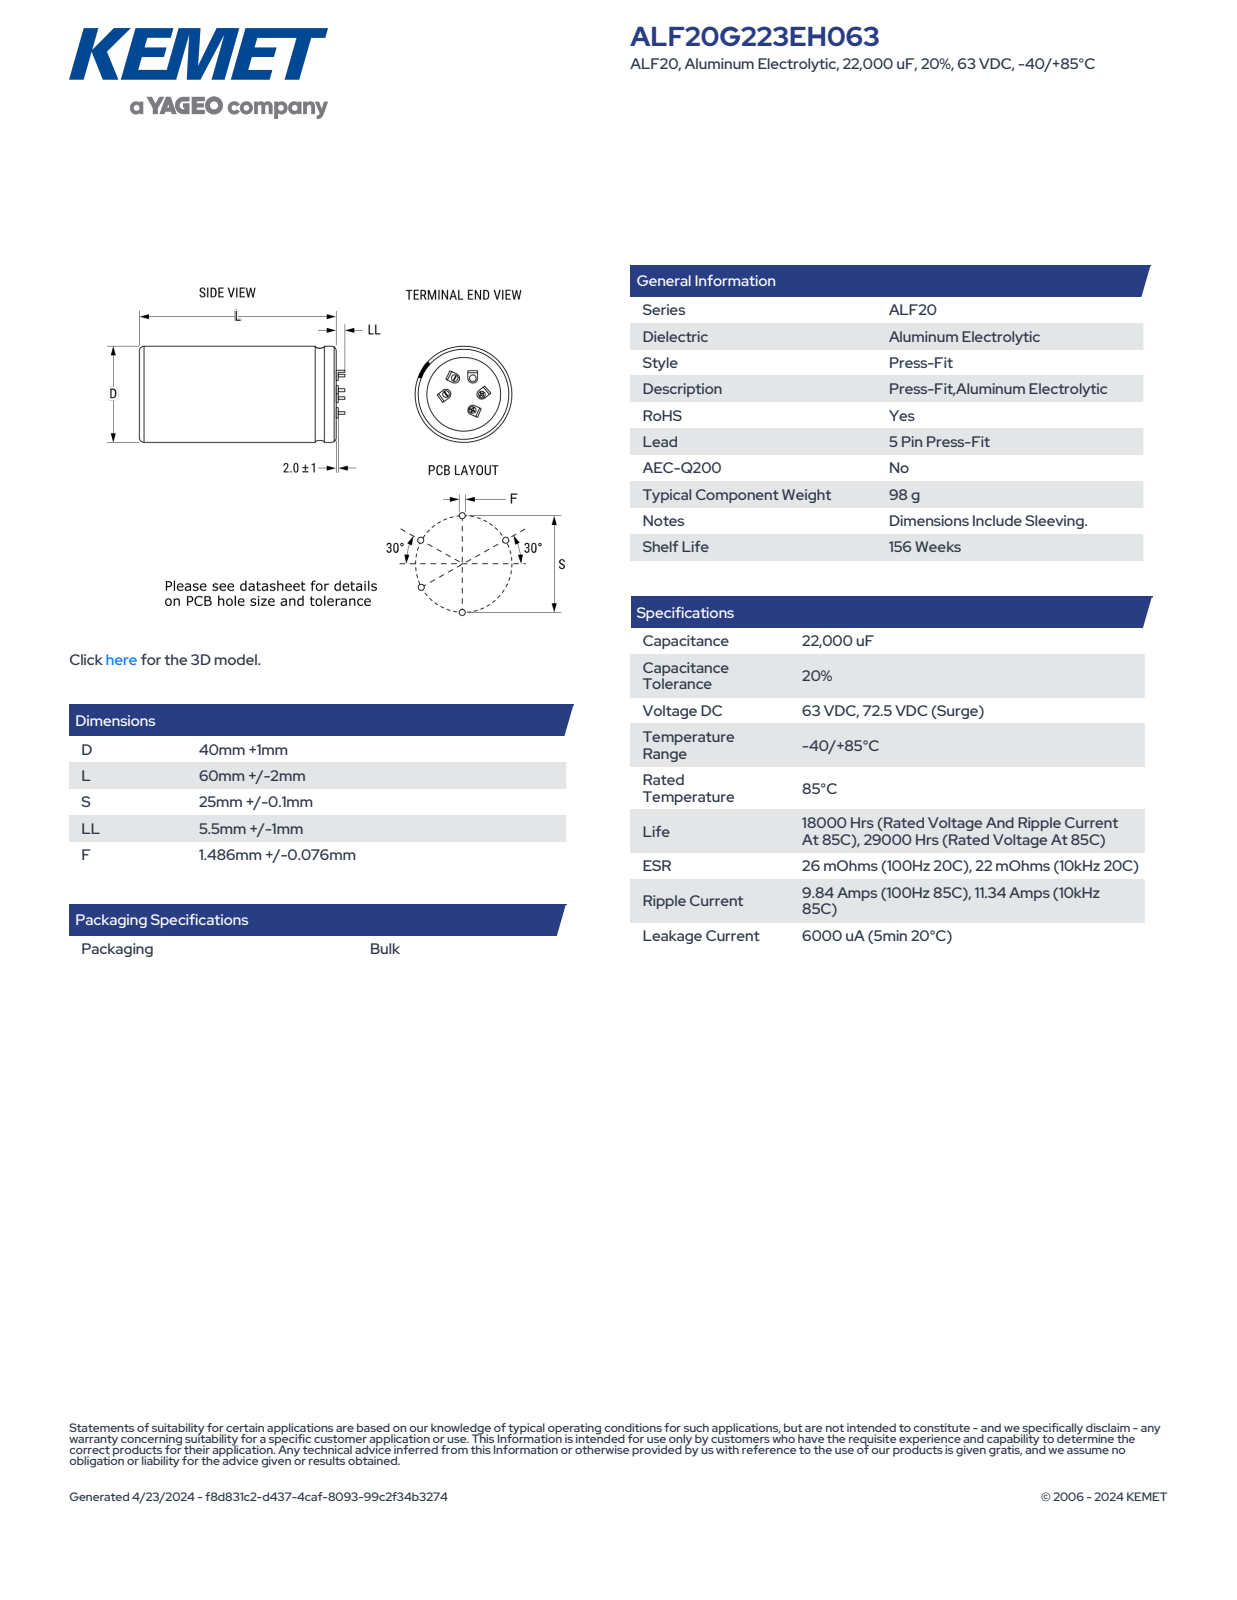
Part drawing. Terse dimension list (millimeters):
name: CARS_ALF2040G_40X60_D41L62S25LL6.5
written by: SolidWorks 2014 (AUTOMOTIVE_DESIGN)
unit: mm
bodies: 6 solids, 395 faces (161 planar, 173 cylindrical, 61 other)
size: 69.41 × 41 × 41
volume: 81 733 mm³; area: 11 062 mm²
bosses: 5× ⌀3.5, 1× ⌀41
rounds: 61× R0.15, 10× R0.1, 10× R0.42, 4× R2.5, 1× R2.52
face distances: 62, 0.8, 62.8, 5, 3, 3.8, 65.8, 4.99, 5.01, 3.6
